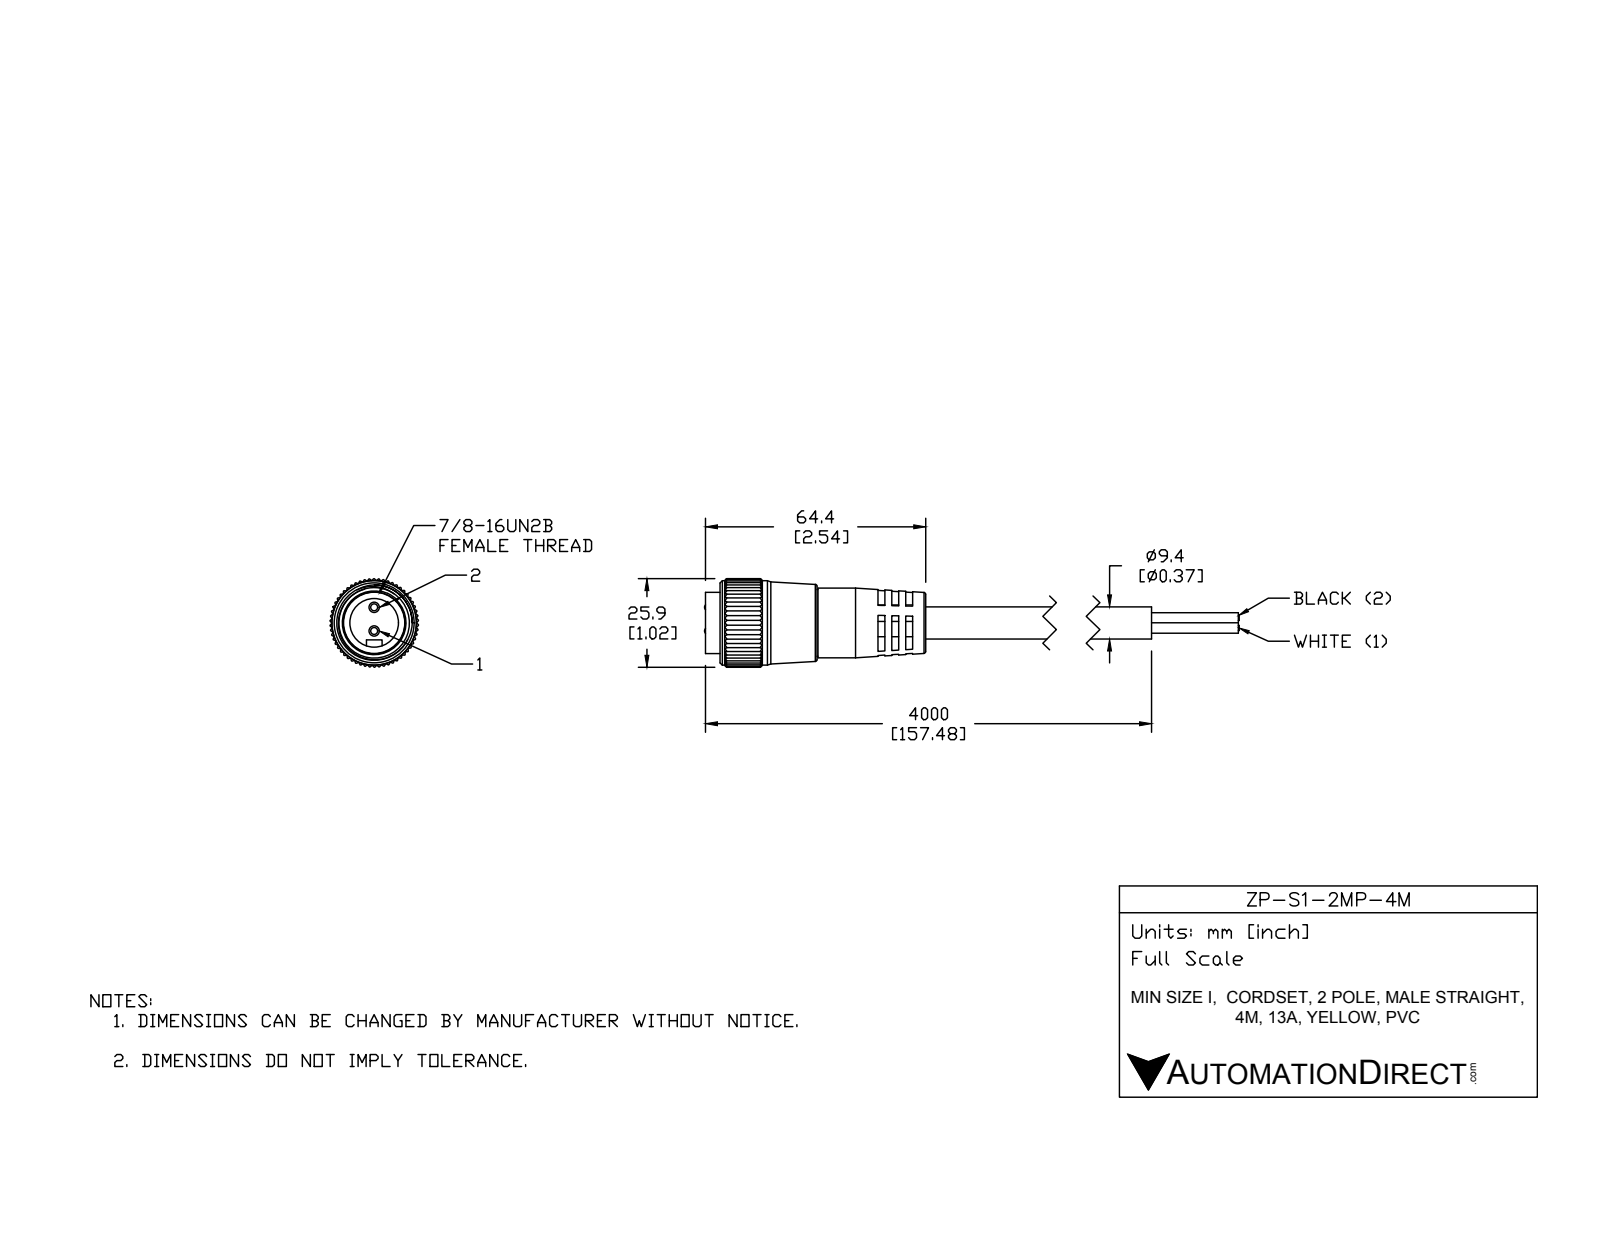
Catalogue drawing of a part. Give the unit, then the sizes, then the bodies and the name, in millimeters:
Units: millimetres
Overall size (bounding box): 109.37 × 52.91 × 25.84
Round holes (diameter × count): ⌀14.22 ×1, ⌀19.96 ×1, ⌀20.45 ×1, ⌀21 ×1
Round bosses / shafts (diameter × count): ⌀9.4 ×2, ⌀3.05 ×2, ⌀2 ×2, ⌀24.68 ×1, ⌀20.4 ×1, ⌀19.5 ×1, ⌀17.88 ×1
Partial cylindrical surfaces — rounded edges, fillets, slot ends (radius × count): R0.25 ×165, R2.29 ×1, R5.25 ×1, R12.93 ×1
Main face-to-face distances: 2, 4.04, 13.88, 11.88, 2.04, 9.84, 6.04, 7.84, 43.53, 45.53
Volume: 26 432 mm³ · Surface area: 12 445 mm²
Bodies: 4 solids, 516 faces (176 planar, 310 cylindrical, 30 other)
Part name (STEP PRODUCT): ZP-S1-2MP-4M
STEP written by: SolidWorks 2015 (AUTOMOTIVE_DESIGN)
